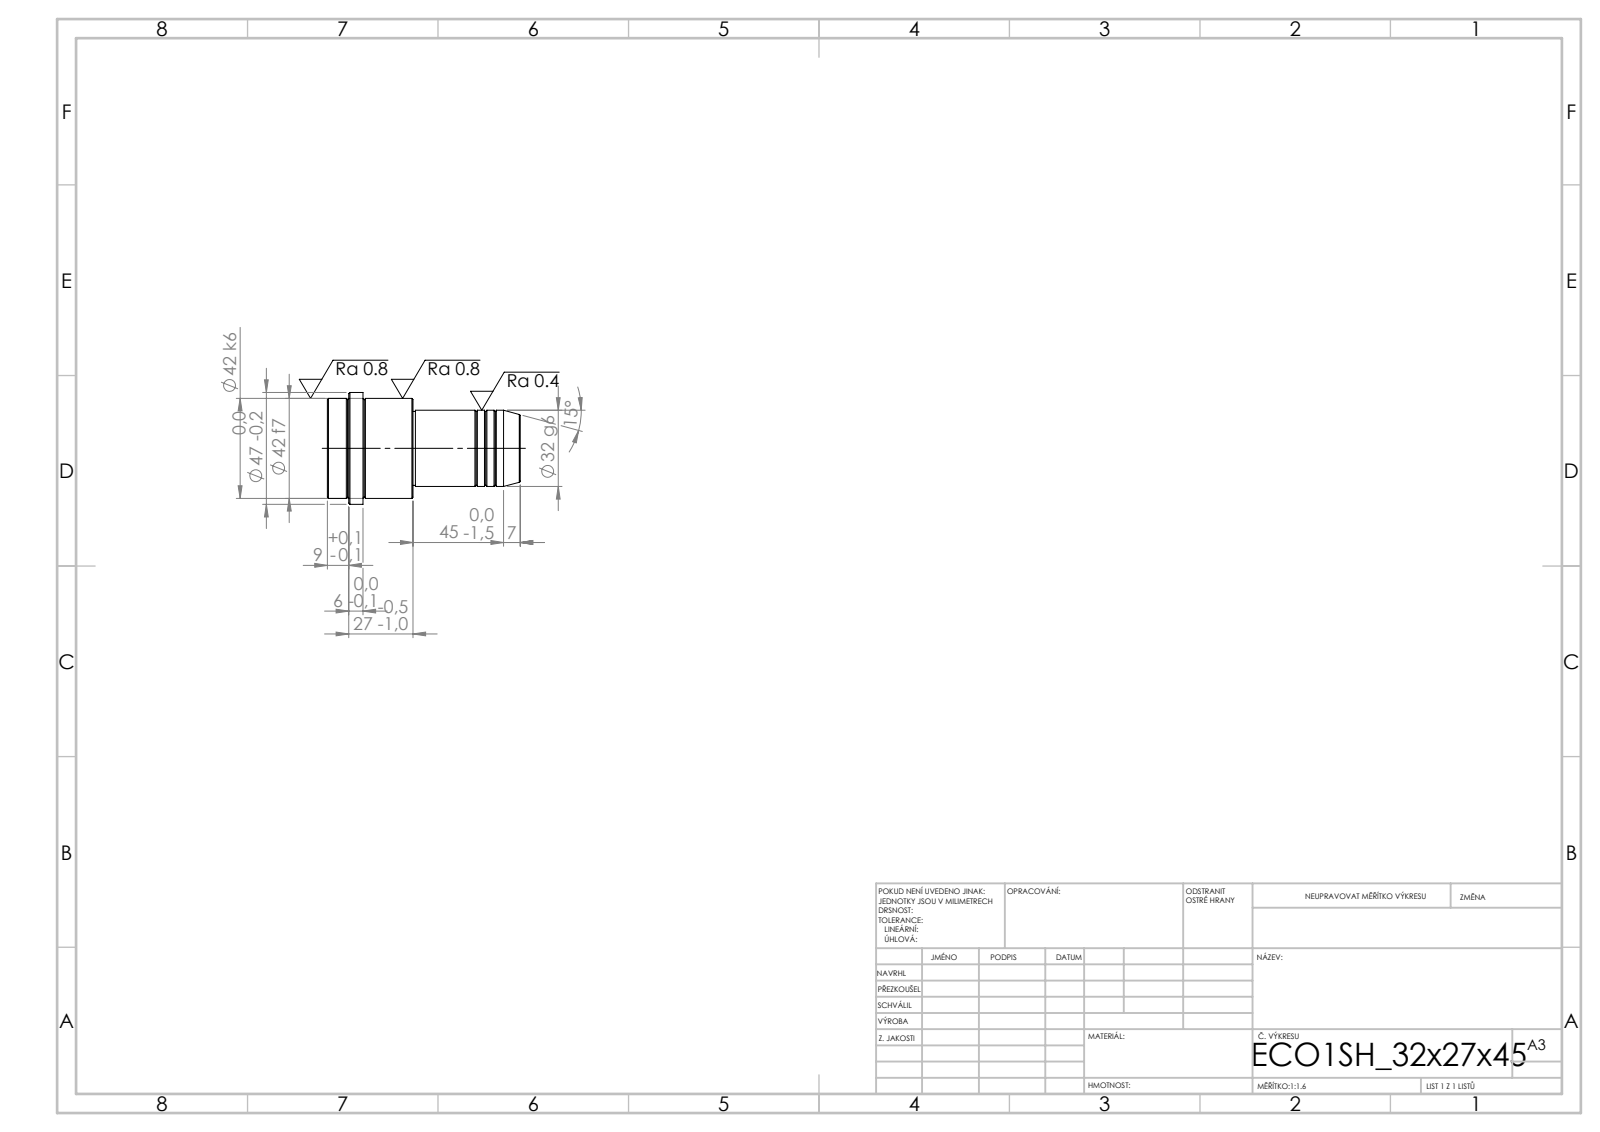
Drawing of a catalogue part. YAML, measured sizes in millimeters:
step_written_by: "SolidWorks 2019 (CONFIG_CONTROL_DESIGN)"
units: millimeters
bodies: {solids: 1, faces: 52, planar: 6, cylindrical: 16, other: 30}
overall_size: [81, 47, 47]
volume: 87207
surface_area: 12914
round_bosses_or_shafts:
  - {diameter: 47, count: 1}
  - {diameter: 42, count: 1}
  - {diameter: 32, count: 1}
  - {diameter: 31, count: 1}
face_to_face_distances: [81, 45, 36, 66, 21, 15, 72, 27, 6, 9]
